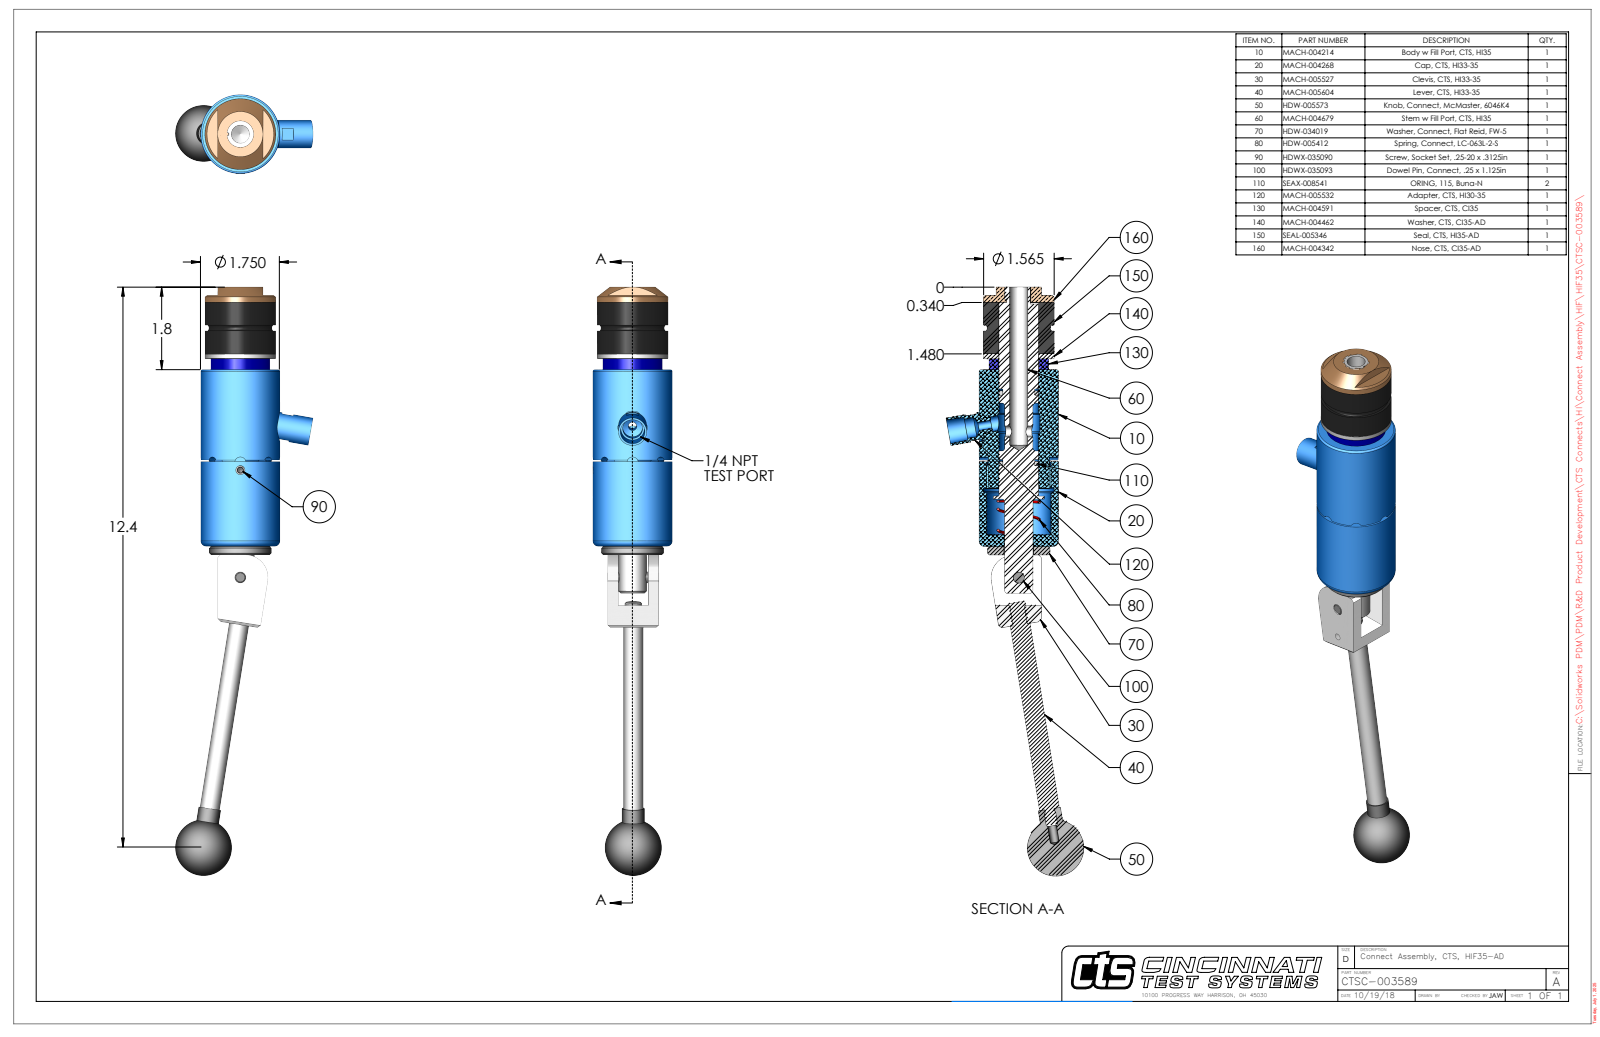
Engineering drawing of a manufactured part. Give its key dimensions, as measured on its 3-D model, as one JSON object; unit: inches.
{"part_name": "CTSC-003589", "step_written_by": "SolidWorks 2023 (AUTOMOTIVE_DESIGN)", "units": "inches", "bodies": {"solids": 10, "faces": 293, "planar": 108, "cylindrical": 120, "other": 65}, "overall_size": [13.042, 3.043, 1.75], "volume_in3": 15.41, "surface_area_in2": 92.32, "round_holes": [[0.201, 2], [0.15, 1], [0.187, 1], [0.249, 1], [0.25, 1], [0.251, 1], [0.313, 1], [0.406, 1], [0.438, 1], [0.531, 1], [0.635, 1], [0.656, 1]], "round_bosses_or_shafts": [[0.25, 2], [1.75, 1], [1.565, 1], [1.565, 1], [1.38, 1], [1.312, 1], [0.869, 1], [0.625, 1]], "partial_cylinders_radius": [[0.125, 4], [0.029, 2], [0.246, 1], [0.33, 1], [0.5, 1], [0.695, 1], [0.833, 1]], "face_to_face_distances": [1.14, 5.405, 4.265, 1.49, 0.35, 3.915, 1.25, 0.11, 0.24, 4.155], "hole_center_spacings": [0.74, 2.376, 3.116]}
